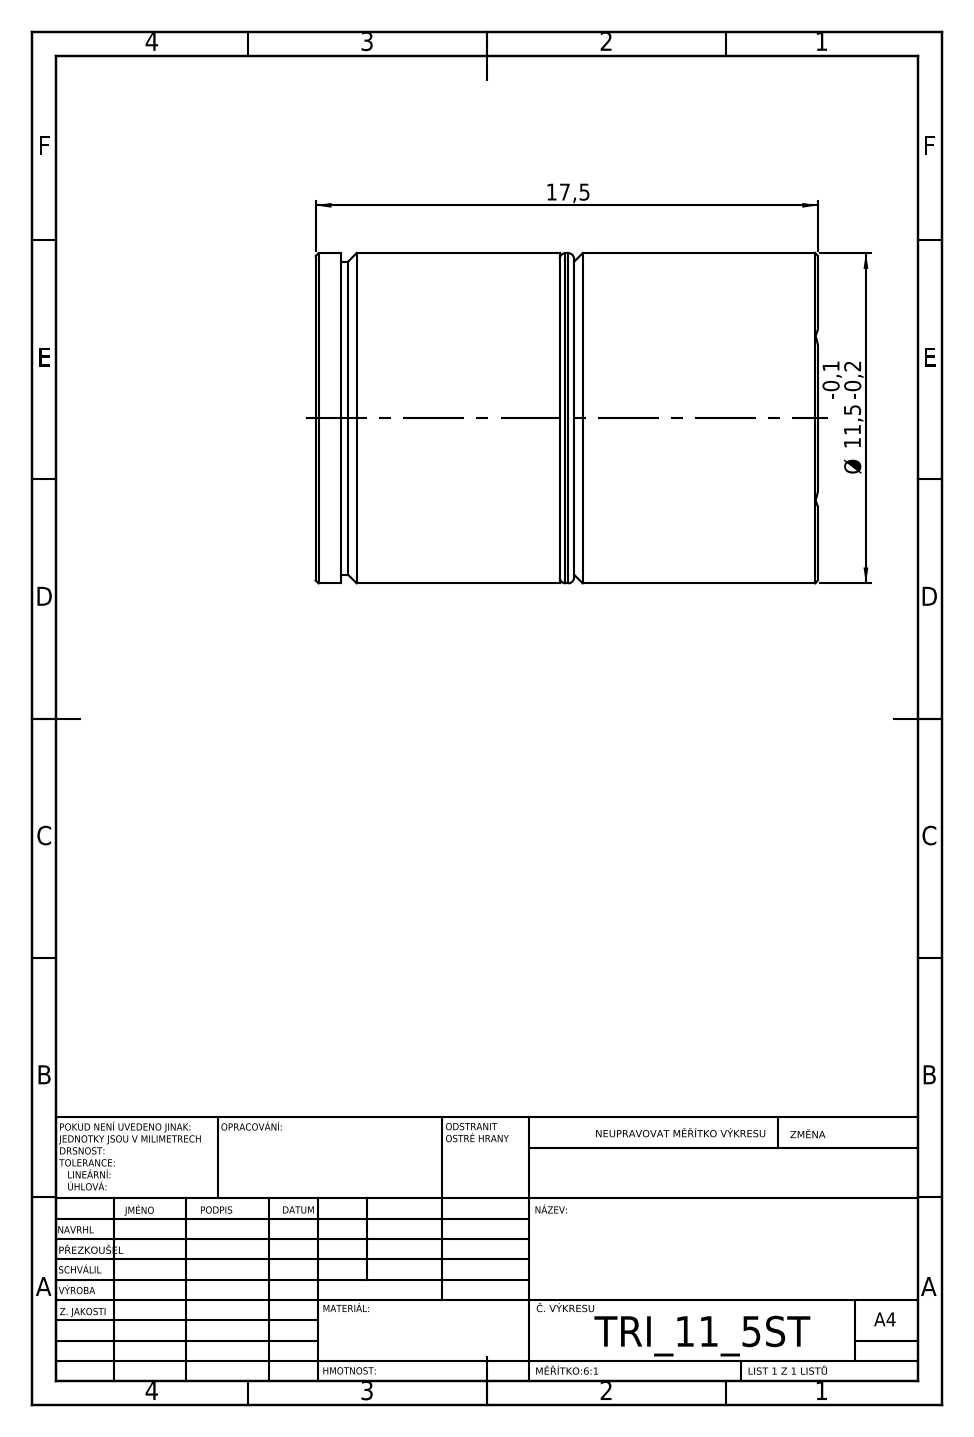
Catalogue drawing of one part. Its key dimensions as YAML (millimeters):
step_written_by: "SolidWorks 2019 (CONFIG_CONTROL_DESIGN)"
units: millimeters
bodies: {solids: 2, faces: 48, planar: 24, cylindrical: 12, other: 12}
overall_size: [17.5, 11.5, 11.5]
volume: 1775
surface_area: 1113
round_bosses_or_shafts:
  - {diameter: 11.5, count: 1}
  - {diameter: 10.9, count: 1}
face_to_face_distances: [8.5, 9, 0.5, 7.5, 8, 16.5, 9.7, 1, 17.5, 16.63]
